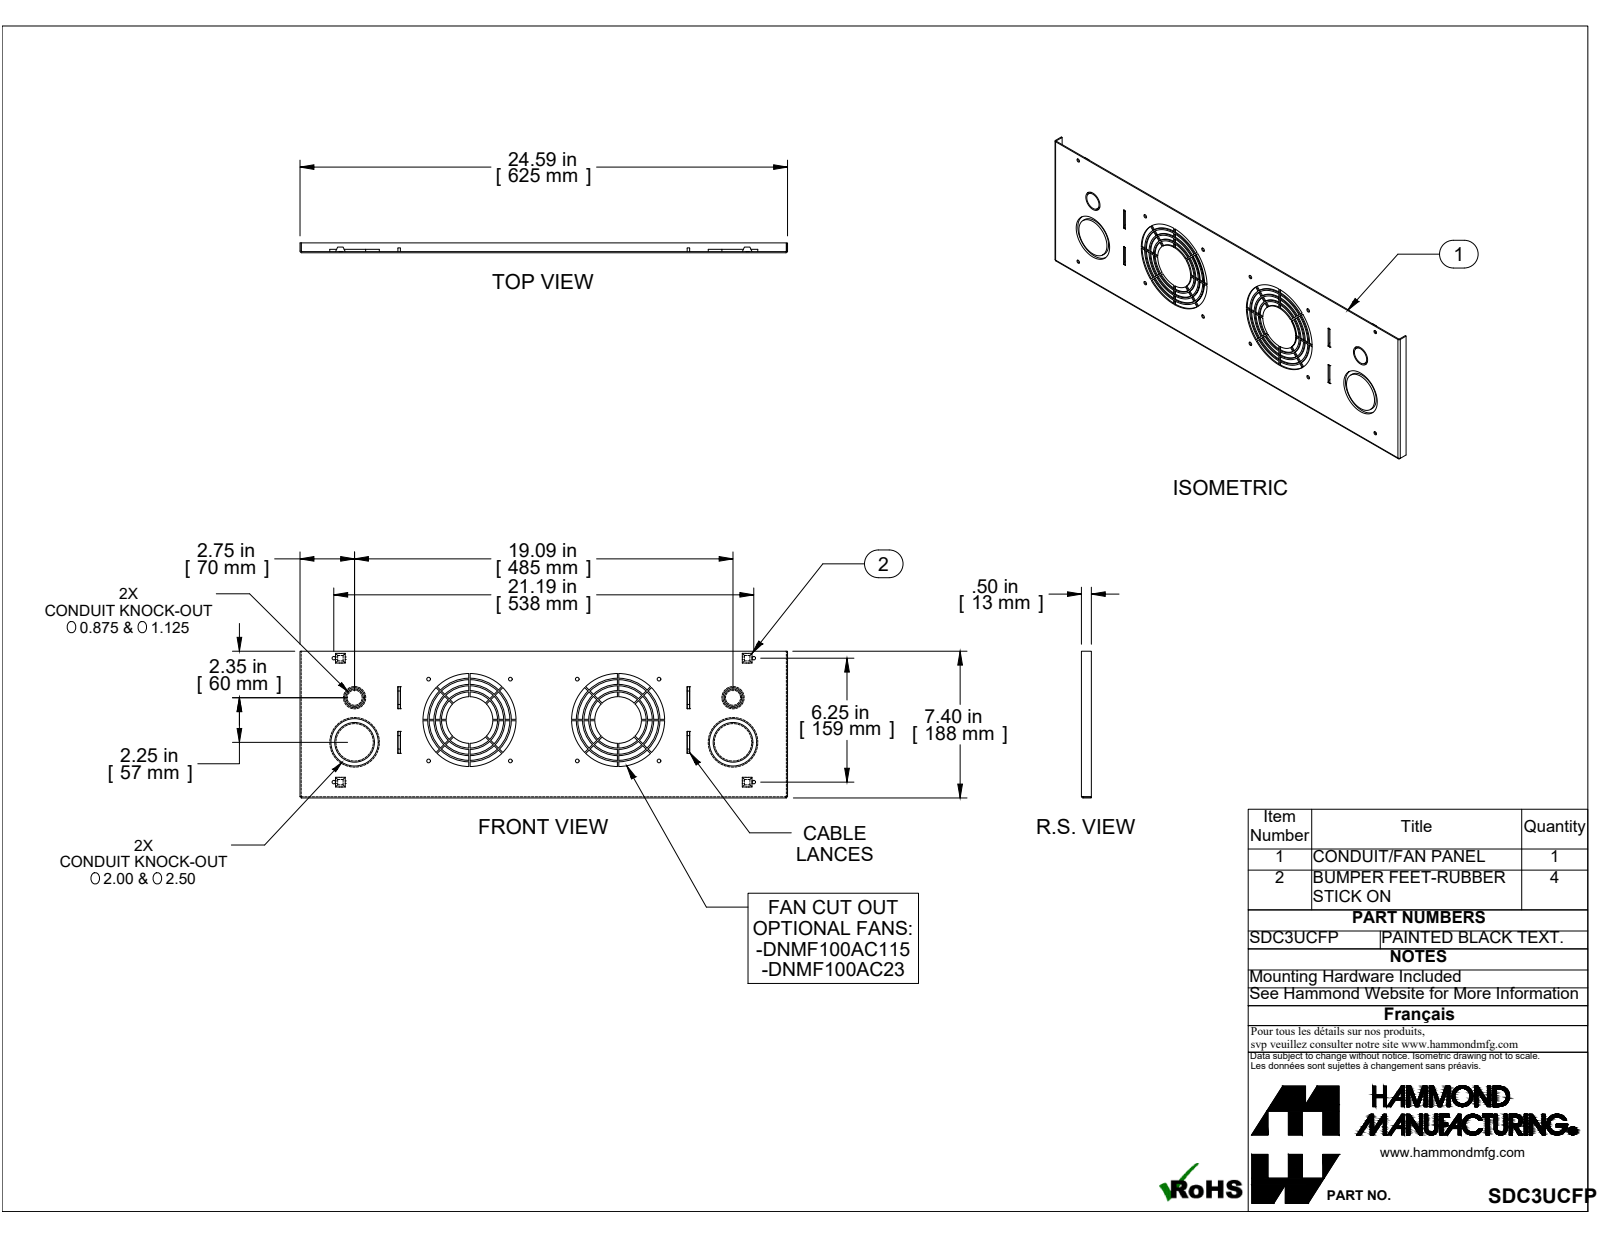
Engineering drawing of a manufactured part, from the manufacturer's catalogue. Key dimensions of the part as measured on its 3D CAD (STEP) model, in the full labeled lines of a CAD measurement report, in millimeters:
Part name (STEP PRODUCT): SDC3UCFP
STEP written by: SolidWorks 2019 (CONFIG_CONTROL_DESIGN)
Units: millimetres
Bodies: 5 solids, 470 faces (288 planar, 178 cylindrical, 4 other)
Overall size (bounding box): 624.7 × 188 × 12.7
Volume: 172 900 mm³ · Surface area: 248 300 mm²
Round holes (diameter × count): ⌀4.8 ×8, ⌀4.5 ×4, ⌀19.3 ×2, ⌀25.7 ×2, ⌀47.9 ×2, ⌀60.6 ×2, ⌀71.8 ×2, ⌀87.6 ×2, ⌀103.4 ×2, ⌀119.2 ×2
Round bosses / shafts (diameter × count): ⌀107 ×2, ⌀91.3 ×2, ⌀75.5 ×2, ⌀63.5 ×2, ⌀59.7 ×2, ⌀50.8 ×2, ⌀28.6 ×2, ⌀22.2 ×2
Partial cylindrical surfaces — rounded edges, fillets, slot ends (radius × count): R1.4 ×8, R0.7 ×3, R2.2 ×3
Main face-to-face distances: 1.4, 3, 1.4, 623.2, 4.4, 1.5, 621.8, 624.7, 12.7, 11.3
Hole centre spacings: 190.5, 74.1, 74.1, 97.8, 104.8, 104.8, 124.7, 147.7
